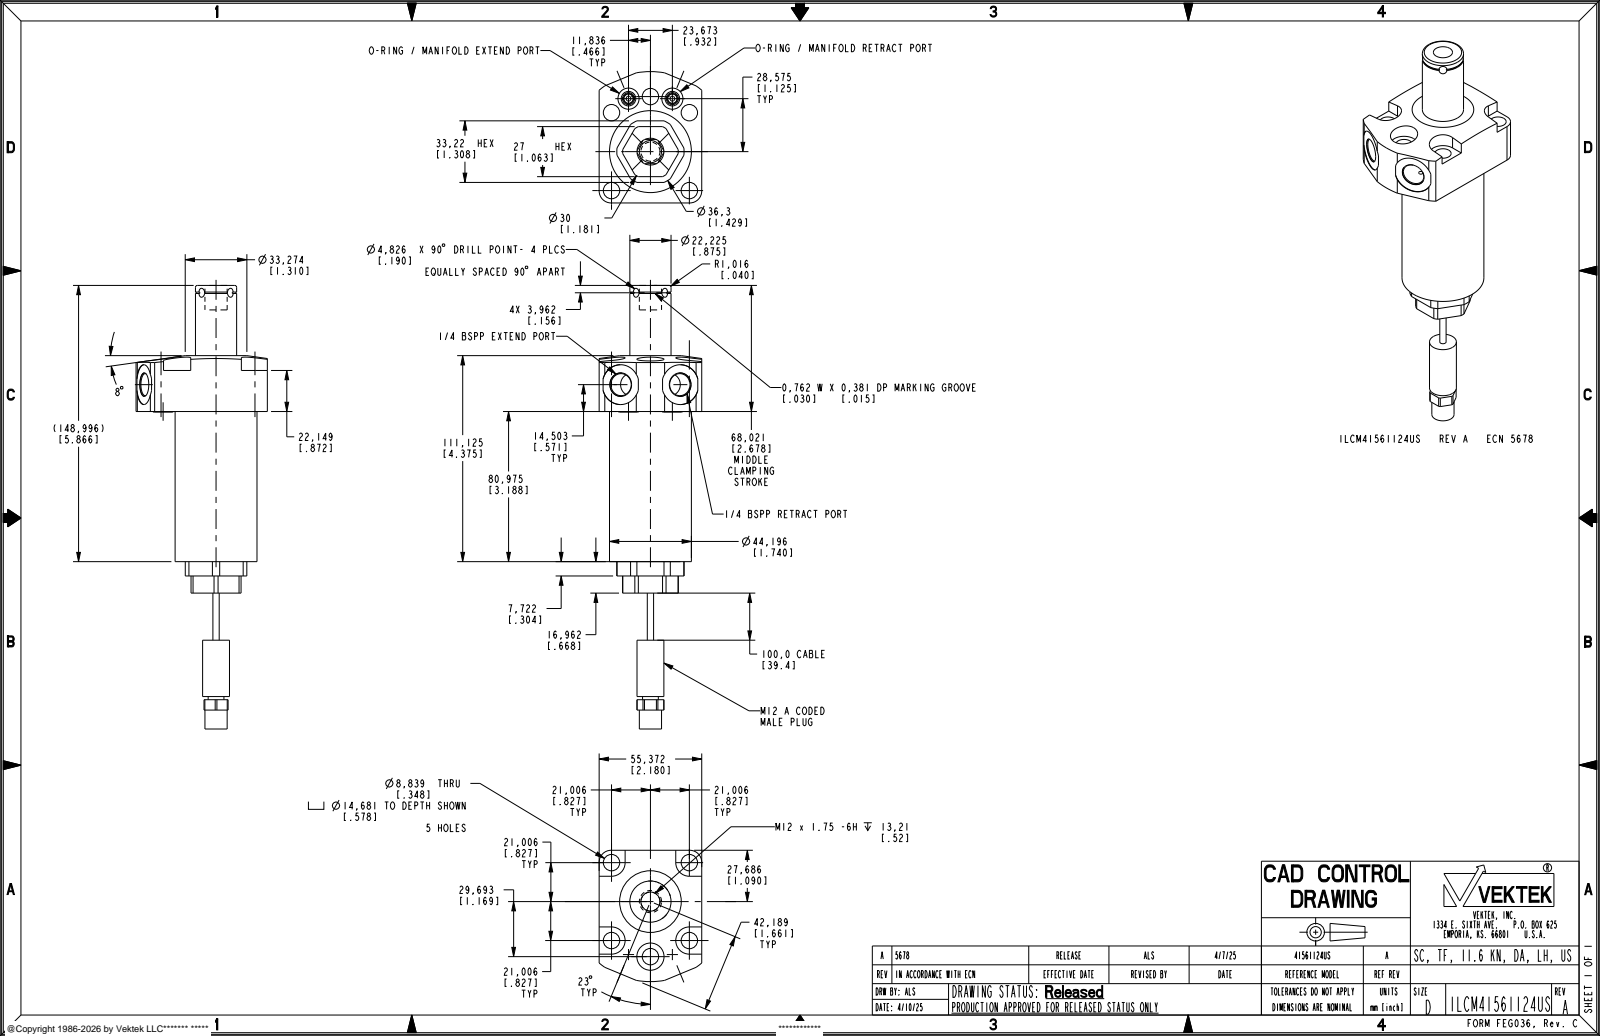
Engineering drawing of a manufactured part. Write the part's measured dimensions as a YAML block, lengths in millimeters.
part_name: "ILCM41561124US"
step_written_by: "CREO PARAMETRIC BY PTC INC, 2021164 (AUTOMOTIVE_DESIGN)"
units: millimeters
bodies: {solids: 1, faces: 205, planar: 88, cylindrical: 87, other: 30}
overall_size: [239.26, 77.22, 60.45]
volume: 248564
surface_area: 39153
round_holes:
  - {diameter: 8.84, count: 5}
  - {diameter: 2.49, count: 2}
  - {diameter: 6.5, count: 2}
  - {diameter: 11.4, count: 2}
  - {diameter: 11.89, count: 2}
  - {diameter: 21.5, count: 2}
  - {diameter: 10.31, count: 1}
  - {diameter: 14.68, count: 1}
  - {diameter: 22.73, count: 1}
round_bosses_or_shafts:
  - {diameter: 5.49, count: 2}
  - {diameter: 44.2, count: 1}
  - {diameter: 22.23, count: 1}
  - {diameter: 14.5, count: 1}
  - {diameter: 11.99, count: 1}
  - {diameter: 11.99, count: 1}
  - {diameter: 8.51, count: 1}
  - {diameter: 3.4, count: 1}
partial_cylinders:
  - {radius: 7.34, count: 4}
  - {radius: 6.48, count: 2}
  - {radius: 10.73, count: 1}
  - {radius: 15, count: 1}
  - {radius: 18.15, count: 1}
  - {radius: 43.18, count: 1}
face_to_face_distances: [55.38, 80.97, 3.11, 30.11, 16.97, 97.94, 120.09, 103.12, 22.15, 128.09]
hole_center_spacings: [29.71, 42.02, 11.88, 11.89, 22.73, 30.93, 33.71, 50.42]
